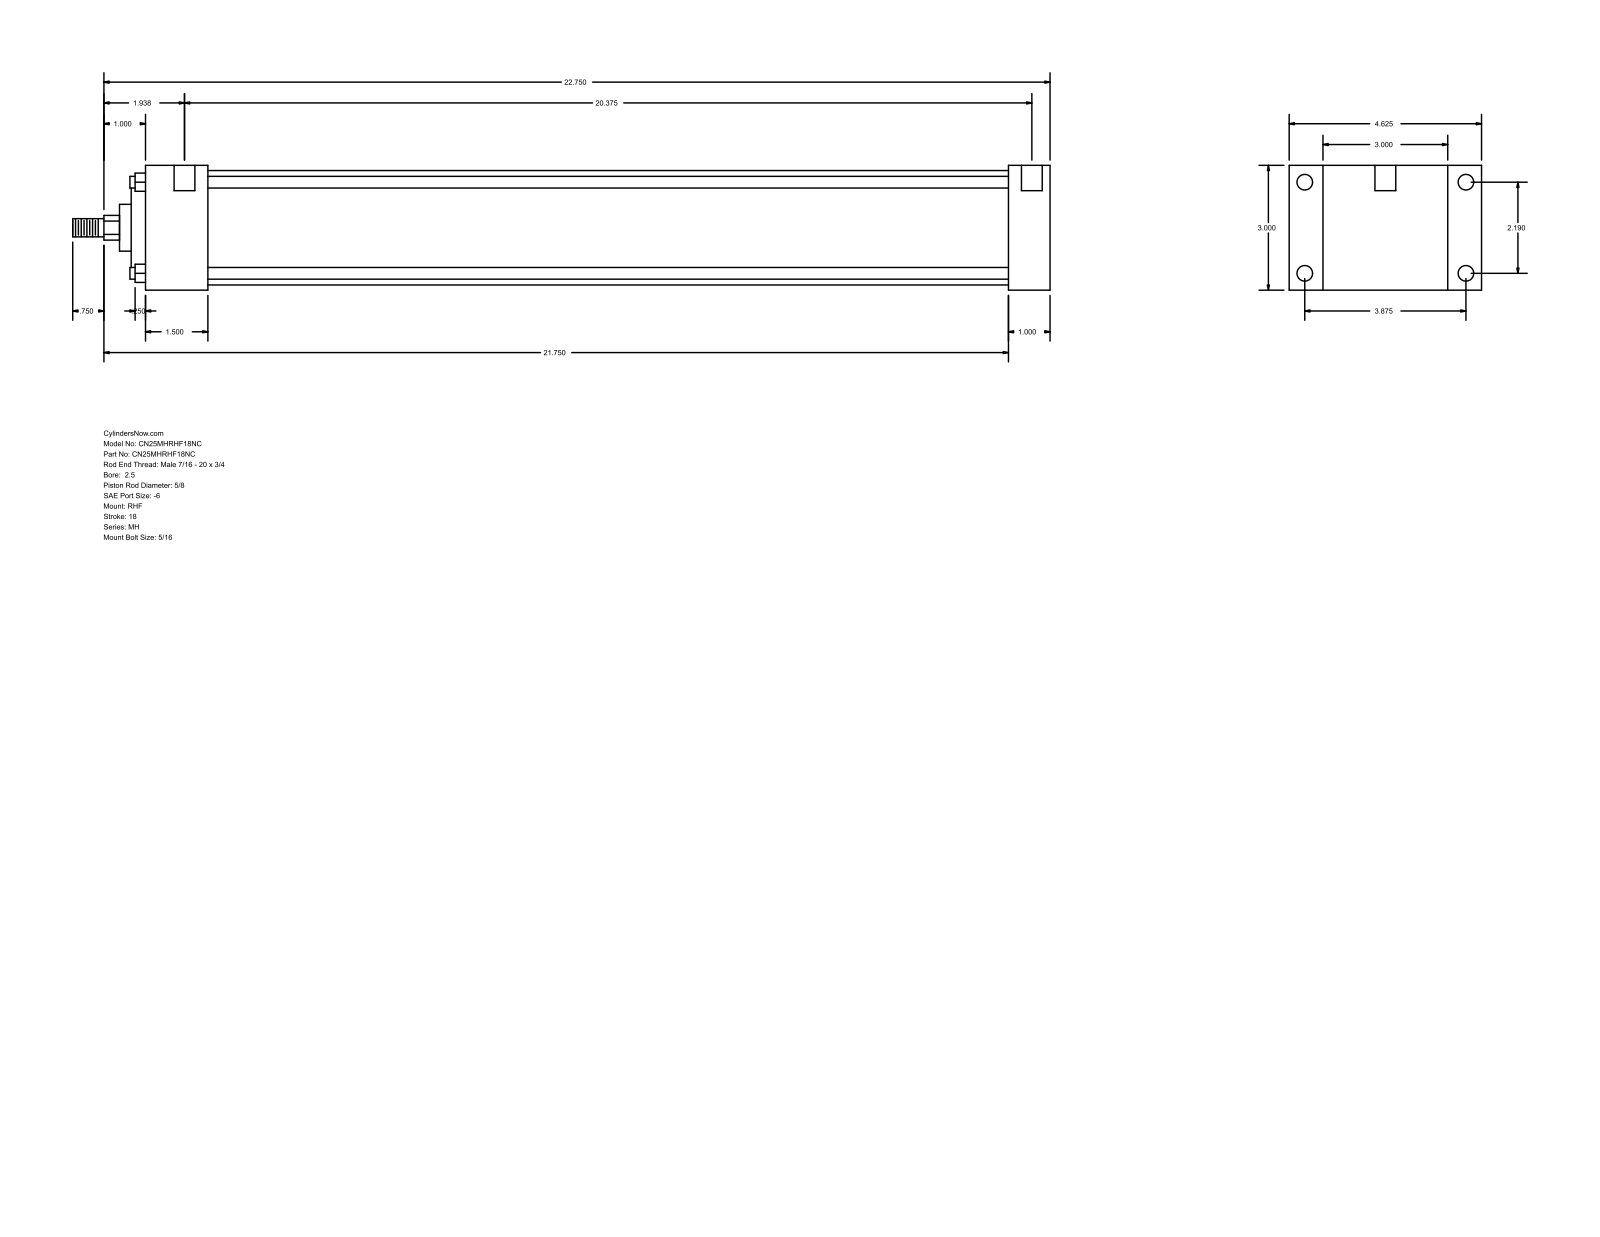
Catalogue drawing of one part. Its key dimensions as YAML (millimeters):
part_name: "MH_RHF__0250_0.625"
step_written_by: "GSSL Pune (CONFIG_CONTROL_DESIGN)"
units: millimeters
bodies: {solids: 0, faces: 90, planar: 61, cylindrical: 29, other: 0}
overall_size: [596.9, 117.47, 76.2]
round_holes:
  - {diameter: 5.56, count: 4}
  - {diameter: 9.53, count: 4}
  - {diameter: 12.7, count: 2}
round_bosses_or_shafts:
  - {diameter: 7.14, count: 4}
  - {diameter: 69.85, count: 1}
  - {diameter: 55.55, count: 1}
  - {diameter: 28.57, count: 1}
  - {diameter: 15.88, count: 1}
  - {diameter: 11.11, count: 1}
partial_cylinders:
  - {radius: 7.54, count: 1}
face_to_face_distances: [76.2, 25.4, 20.64, 96.84, 552.45, 527.05, 38.1, 117.48, 488.95, 514.35]
hole_center_spacings: [55.62, 98.42, 113.05, 525.46, 3.17, 4.76, 517.53, 520.7]
